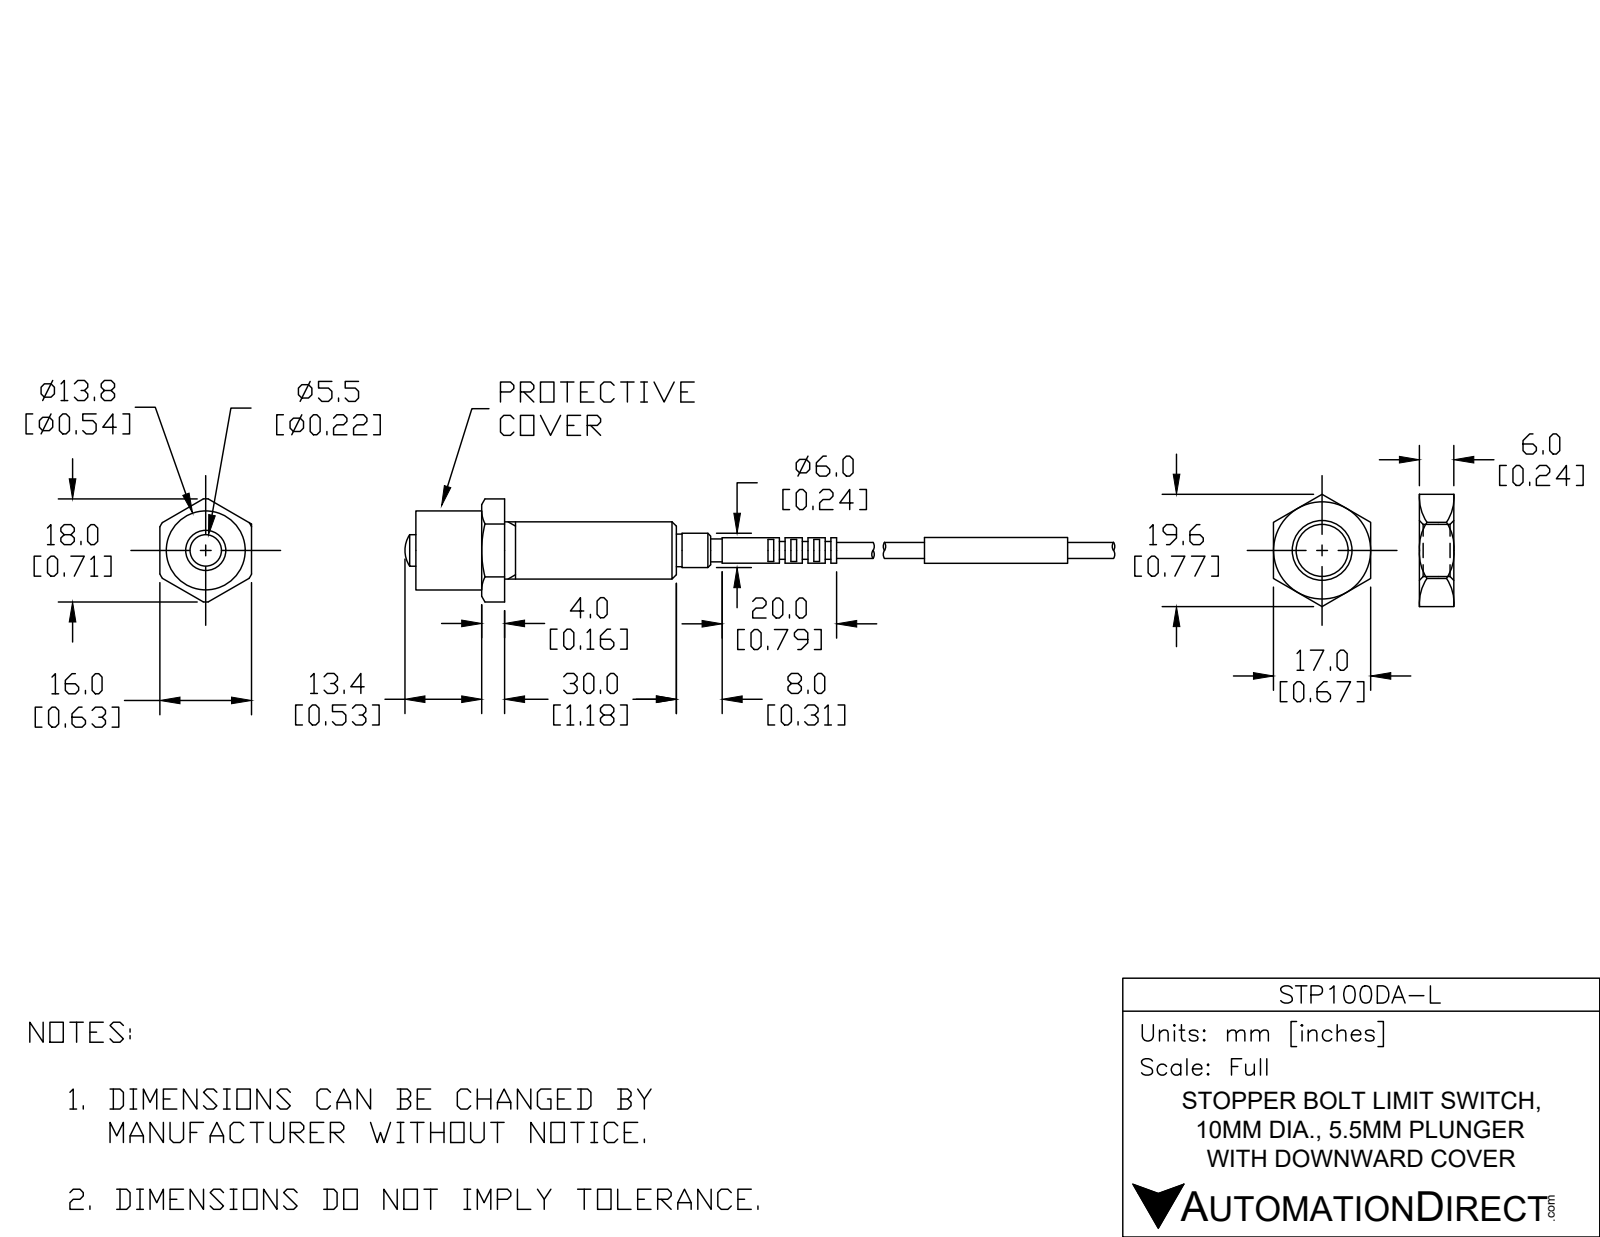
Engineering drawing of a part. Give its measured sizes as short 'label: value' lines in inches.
name: STP100DA-L
written by: SolidWorks 2017 (CONFIG_CONTROL_DESIGN)
unit: in
bodies: 2 solids, 169 faces (68 planar, 81 cylindrical, 20 other)
size: 4.976 × 0.709 × 0.63
volume: 0.342 in³; area: 5.572 in²
bosses: 1× ⌀0.543, 1× ⌀0.394, 1× ⌀0.236, 1× ⌀0.224, 1× ⌀0.217, 1× ⌀0.177, 1× ⌀0.175, 1× ⌀0.157
rounds: 1× R0.354
face distances: 0.61, 0.63, 0.157, 0.039, 0.079, 0.118, 0.236, 0.197, 0.453, 0.276
